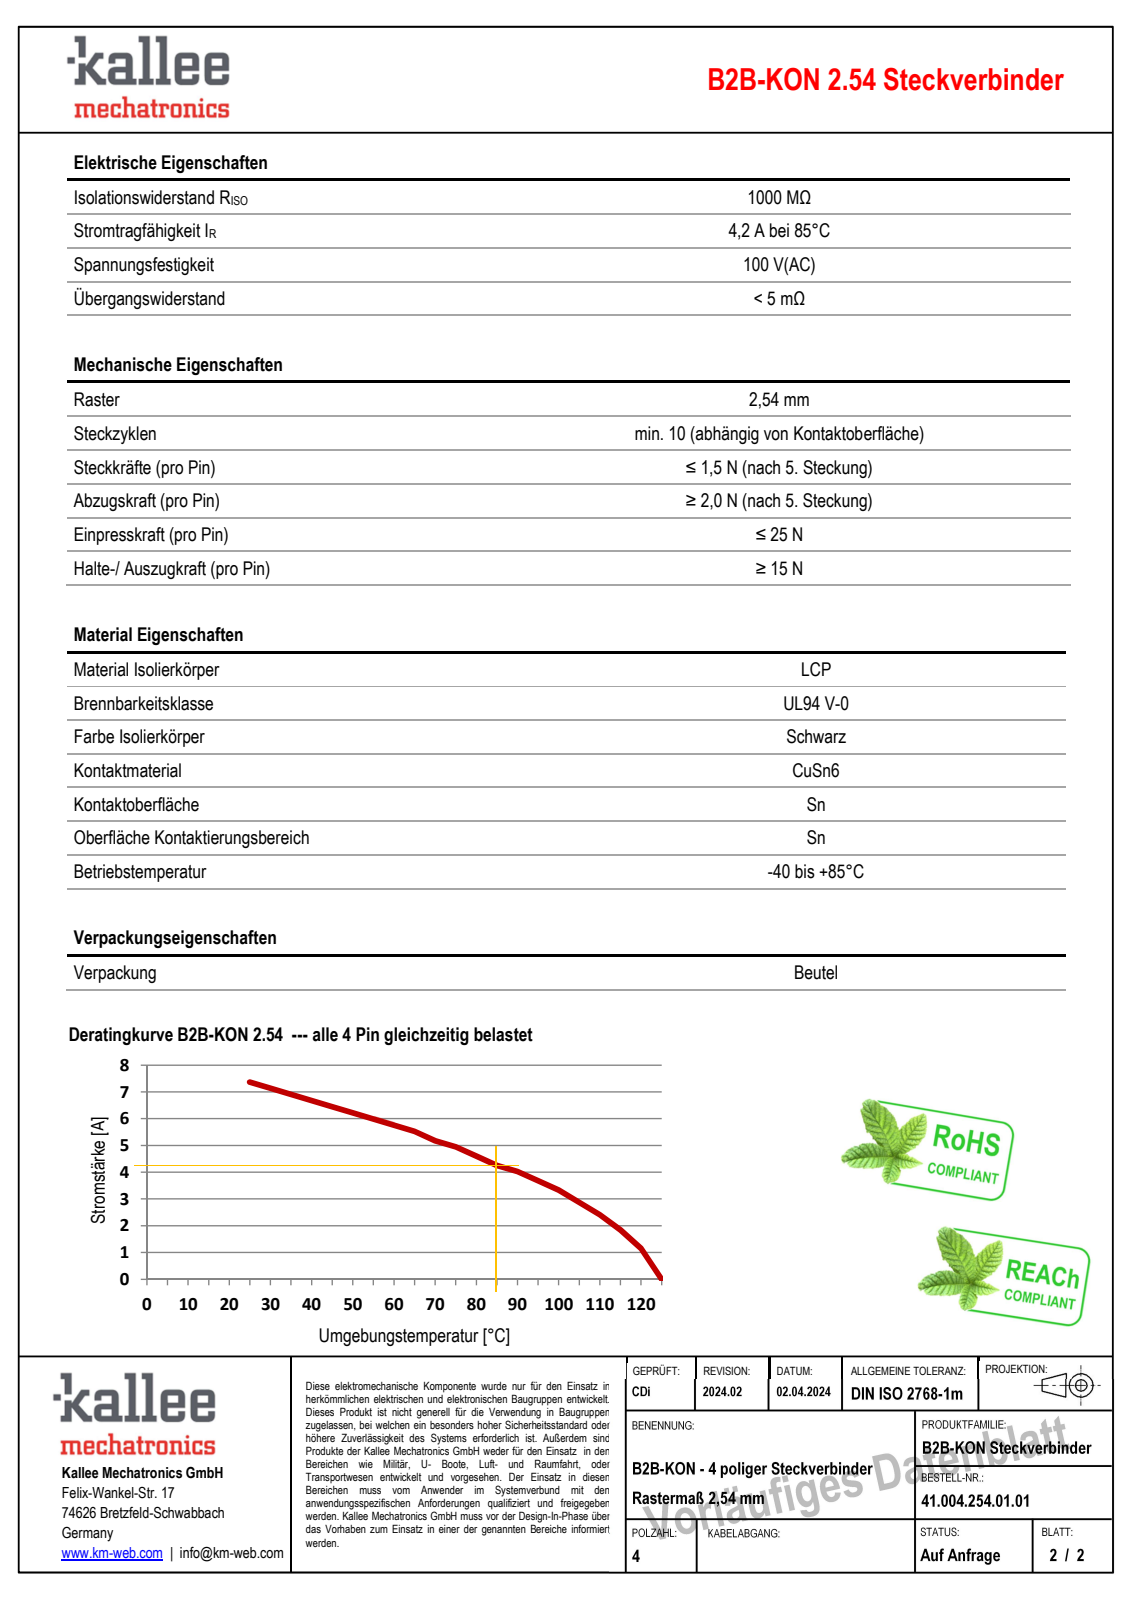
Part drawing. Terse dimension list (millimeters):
name: B2B-KON_41.04.254.01.01 v2
written by: Autodesk Translation Framework v12.20.1.177 (AUTOMOTIVE_DESIGN)
unit: mm
bodies: 1 solid, 216 faces (96 planar, 118 cylindrical, 2 other)
size: 15 × 5.08 × 5
volume: 173 mm³; area: 274 mm²
bosses: 1× ⌀1.2
rounds: 20× R1, 14× R3, 8× R3.22, 4× R1.22, 2× R0.1, 2× R0.17, 2× R0.18, 2× R0.2
face distances: 0.5, 4.5, 5.08, 2.54, 4, 7, 0.4, 1.43, 3.57, 0.93
